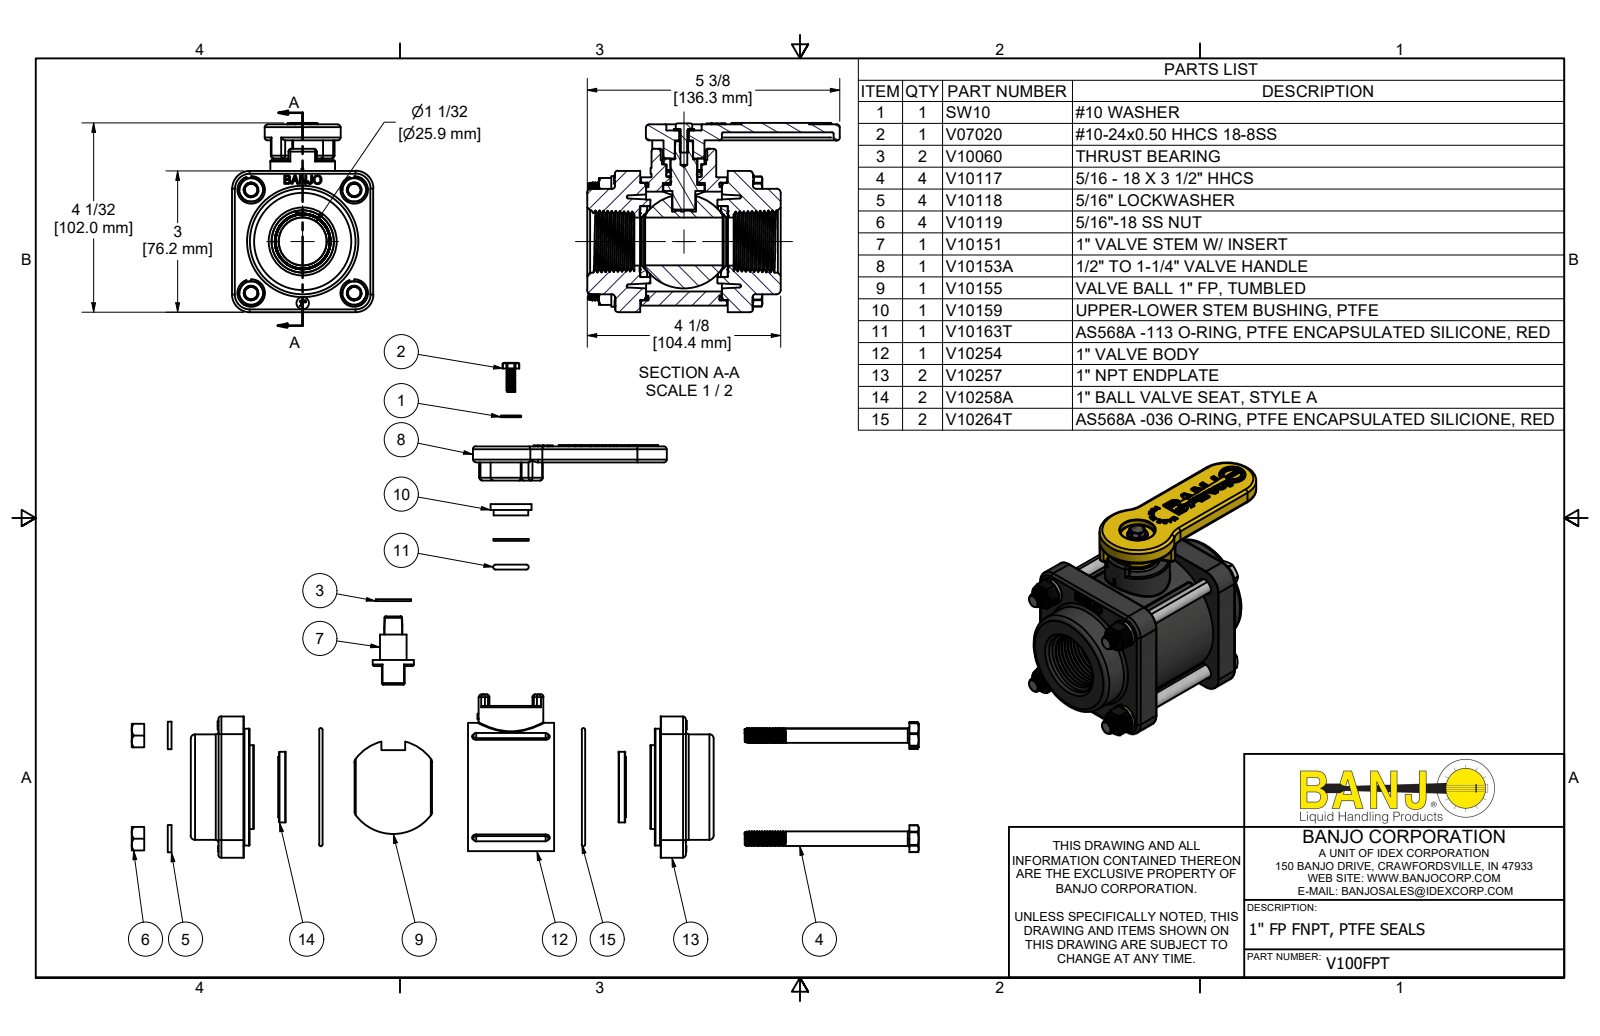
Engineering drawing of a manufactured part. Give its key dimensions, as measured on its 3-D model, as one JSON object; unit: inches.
{"part_name": "V100FPT; V10117; V10254; V10118 (+8 more)", "step_written_by": "Autodesk Inventor 2022 (AUTOMOTIVE_DESIGN)", "units": "inches", "bodies": {"solids": 28, "faces": 2072, "planar": 717, "cylindrical": 623, "other": 732}, "overall_size": [5.365, 4.017, 3], "volume_in3": 22.08, "surface_area_in2": 197.3, "round_holes": [[0.252, 4], [0.322, 4], [0.365, 4], [0.089, 1], [0.145, 1], [0.2, 1], [0.203, 1], [0.26, 1], [0.376, 1], [0.531, 1], [0.562, 1], [0.572, 1]], "round_bosses_or_shafts": [[0.268, 60], [0.583, 4], [0.313, 4], [2.725, 1], [2.482, 1], [2.302, 1], [2.24, 1], [1.78, 1]], "partial_cylinders_radius": [[0.06, 58], [0.03, 32], [0.031, 12], [0.134, 8], [0.015, 4], [0.078, 4], [0.284, 4], [0.375, 4]], "face_to_face_distances": [0.125, 1.735, 3, 1.25, 2.93, 0.535, 2.395, 1.86, 2.395, 0.535], "hole_center_spacings": [1.55, 2.192, 1.117, 2.644, 3.1, 0.364, 1.31, 2.569]}
